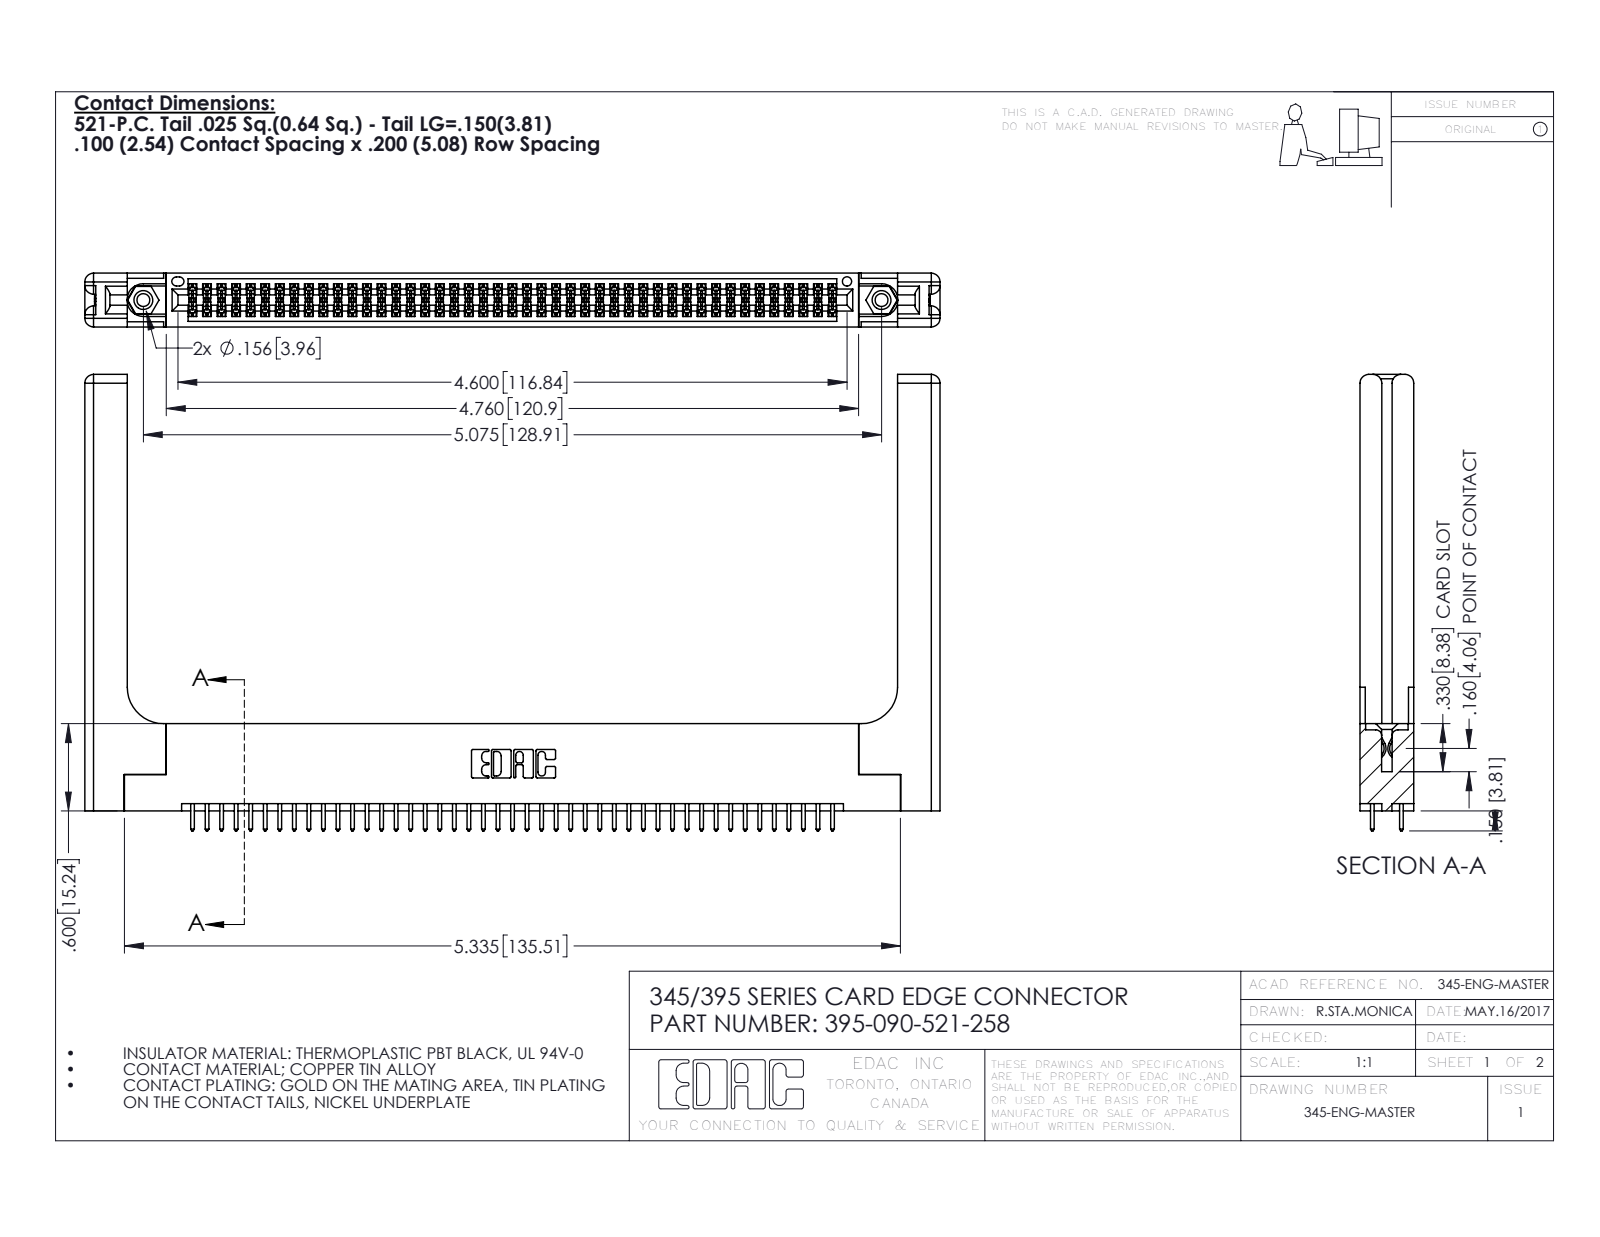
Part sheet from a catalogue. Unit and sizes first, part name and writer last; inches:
Units: inches
Overall size (bounding box): 5.879 × 3.137 × 0.37
Round holes (diameter × count): ⌀0.089 ×2, ⌀0.125 ×2, ⌀0.156 ×2, ⌀0.064 ×1
Round bosses / shafts (diameter × count): ⌀0.155 ×2
Partial cylindrical surfaces — rounded edges, fillets, slot ends (radius × count): R0.006 ×135, R0.01 ×90, R0.01 ×22, R0.06 ×16, R0.007 ×6, R0.031 ×6, R0.026 ×3, R0.014 ×2
Main face-to-face distances: 0.072, 0.298, 0.37, 0.2, 0.098, 0.272, 0.025, 0.225, 0.148, 0.15
Hole centre spacings: 0.27, 4.839, 5.075
Volume: 1.402 in³ · Surface area: 40.78 in²
Bodies: 95 solids, 4882 faces (3198 planar, 1624 cylindrical, 60 other)
Part name (STEP PRODUCT): 345-250-001_345-250-001-102; 345-292-001_345-293-121; 345-220-058_345-220-058; 395-090-521-258 (+1 more)
STEP written by: SolidWorks 2016 (CONFIG_CONTROL_DESIGN)
